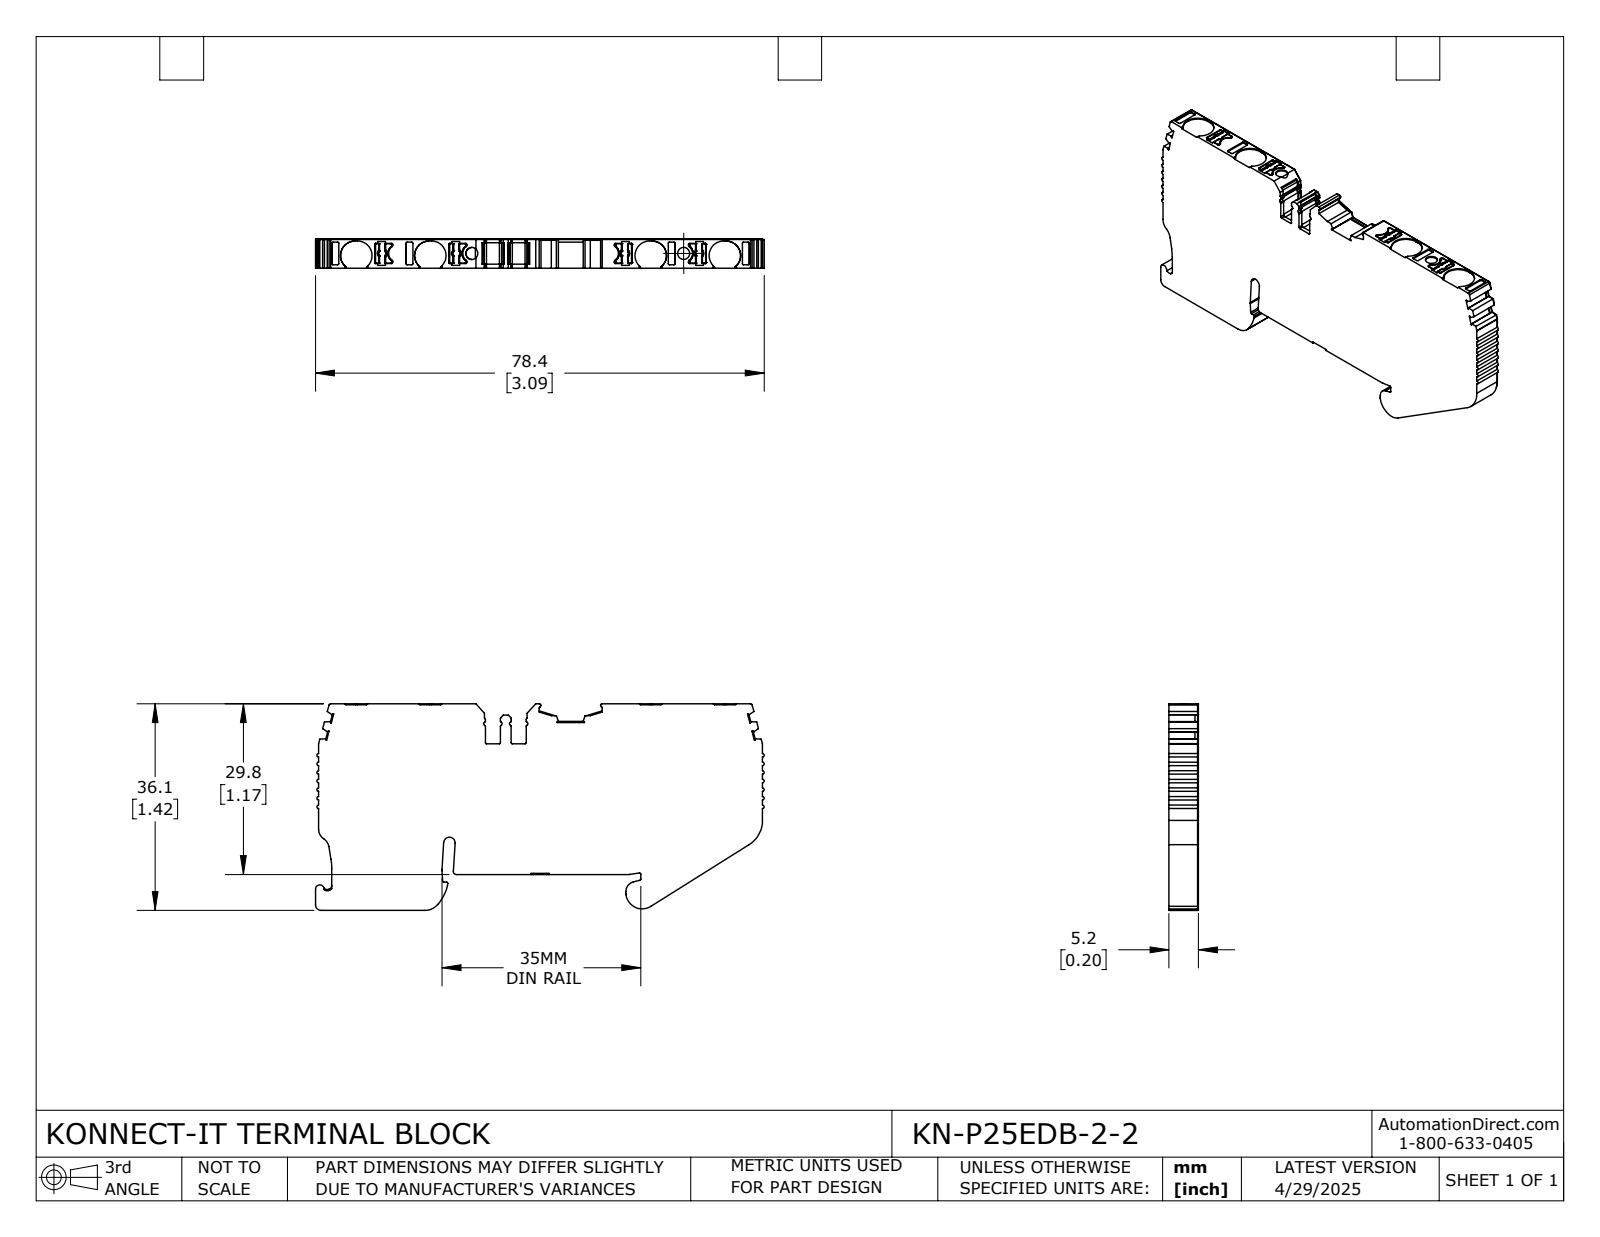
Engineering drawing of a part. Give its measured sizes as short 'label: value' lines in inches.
name: KN-P25EDB-2-2
written by: SolidWorks 2024 (CONFIG_CONTROL_DESIGN)
unit: in
bodies: 1 solid, 743 faces (381 planar, 291 cylindrical, 71 other)
size: 3.085 × 1.42 × 0.203
volume: 0.731 in³; area: 9.637 in²
holes: 2× ⌀0.083
rounds: 78× R0.008, 39× R0.012, 21× R0.004, 18× R0.02, 16× R0.006, 9× R0.016, 8× R0.1, 4× R0.059
face distances: 0.203, 1.166, 1.174, 0.246, 1.412, 1.42, 3.052, 0.047, 0.197, 0.177
hole spacings: 1.456
